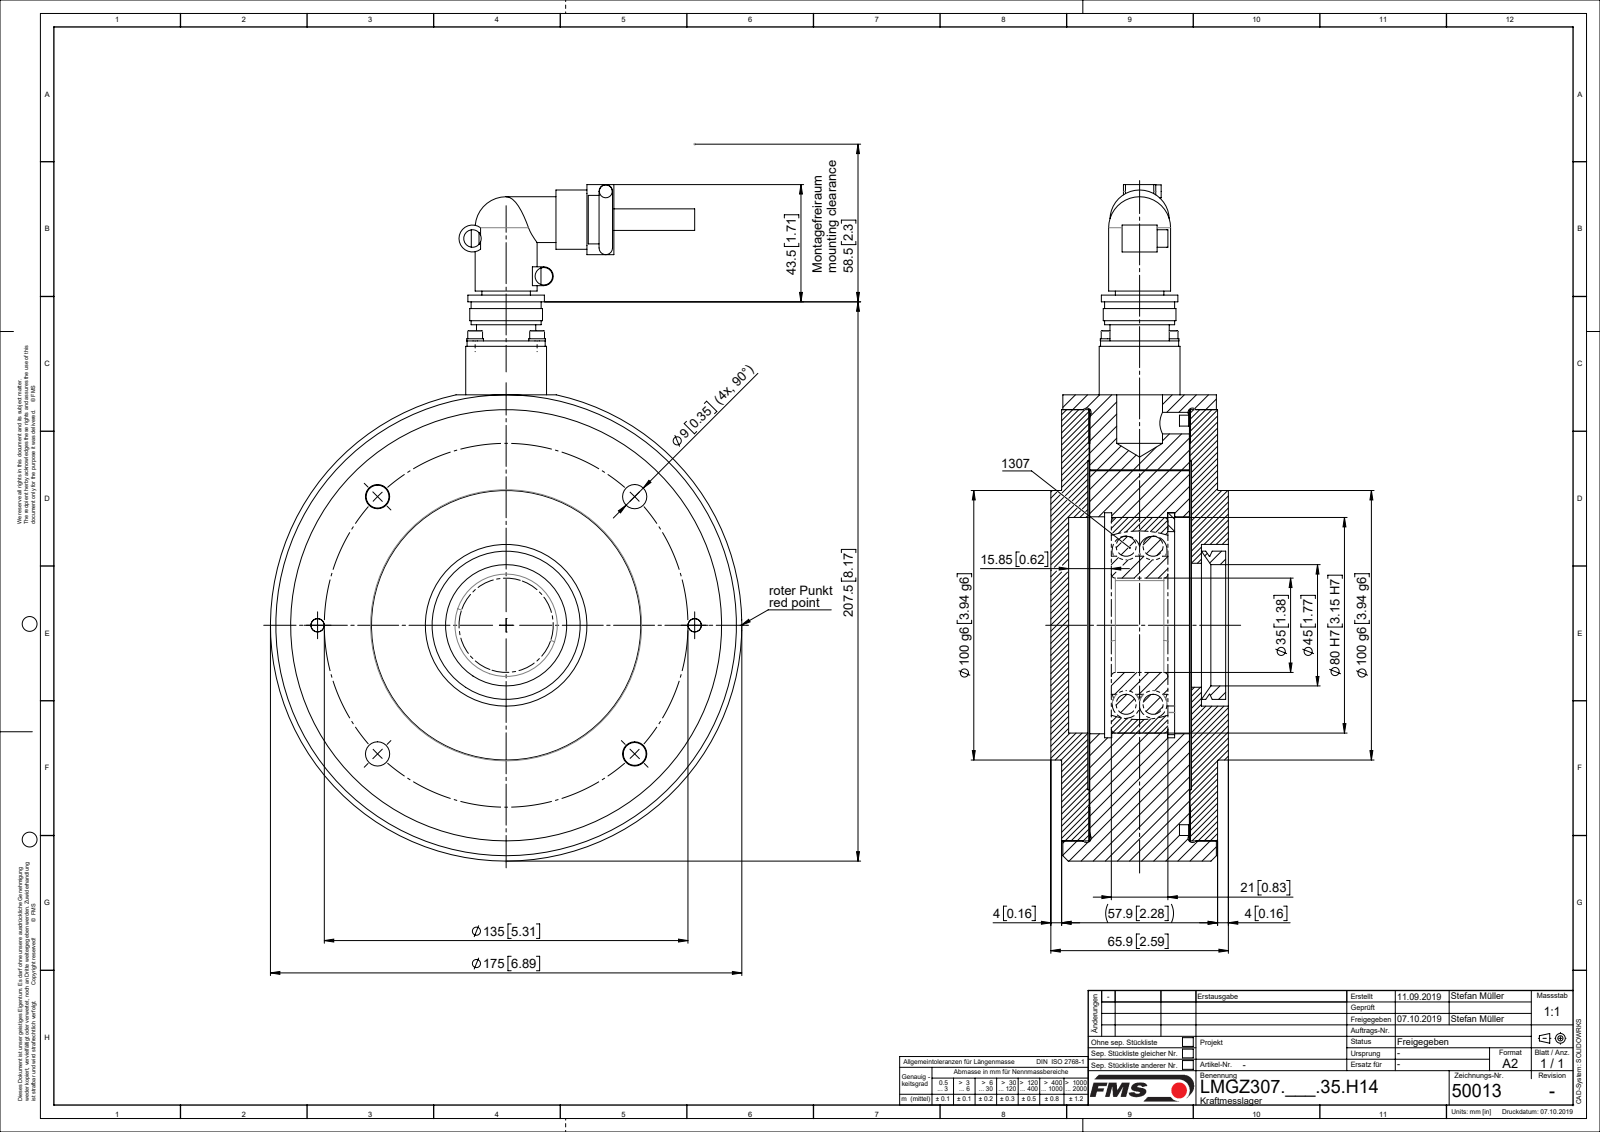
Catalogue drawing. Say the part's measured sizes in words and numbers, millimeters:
The part is named "L50013; L4857104; TEIL1; L48573 (+8 more)". Its 3-D file was written by "Mechanical Desktop 2007 (CONFIG_CONTROL_DESIGN)". It is 22 solids with 401 faces: 111 planar, 233 cylindrical and 57 other. Overall it measures 317.5 by 251 by 104.7 millimeters. Its volume is 1 294 000 cubic millimeters and its surface area 272 533 square millimeters. Round holes: 4 of diameter 2.6, 4 of diameter 3.2, 4 of diameter 3.4, 4 of diameter 3.5, 4 of diameter 9, 2 of diameter 5, 2 of diameter 6.6, 2 of diameter 8.68, 2 of diameter 11, 1 of diameter 8, 1 of diameter 10, 1 of diameter 23. Round bosses or shafts: 4 of diameter 6.2, 4 of diameter 5.5, 4 of diameter 3, 2 of diameter 22, 2 of diameter 10, 2 of diameter 6.5, 2 of diameter 6, 2 of diameter 4.8. Partial cylindrical surfaces (rounded edges, fillets, slot ends): 2 of radius 2.5, 2 of radius 7.5, 1 of radius 3.5, 1 of radius 5. The main face-to-face distances are 37.25, 10.2, 10.45, 47.45, 47.7, 37, 0.5, 38, 9.7, 48.2. The hole center spacings are 16.26, 23, 48.72, 52.67, 67.5, 95.46, 115.55, 127.04.
